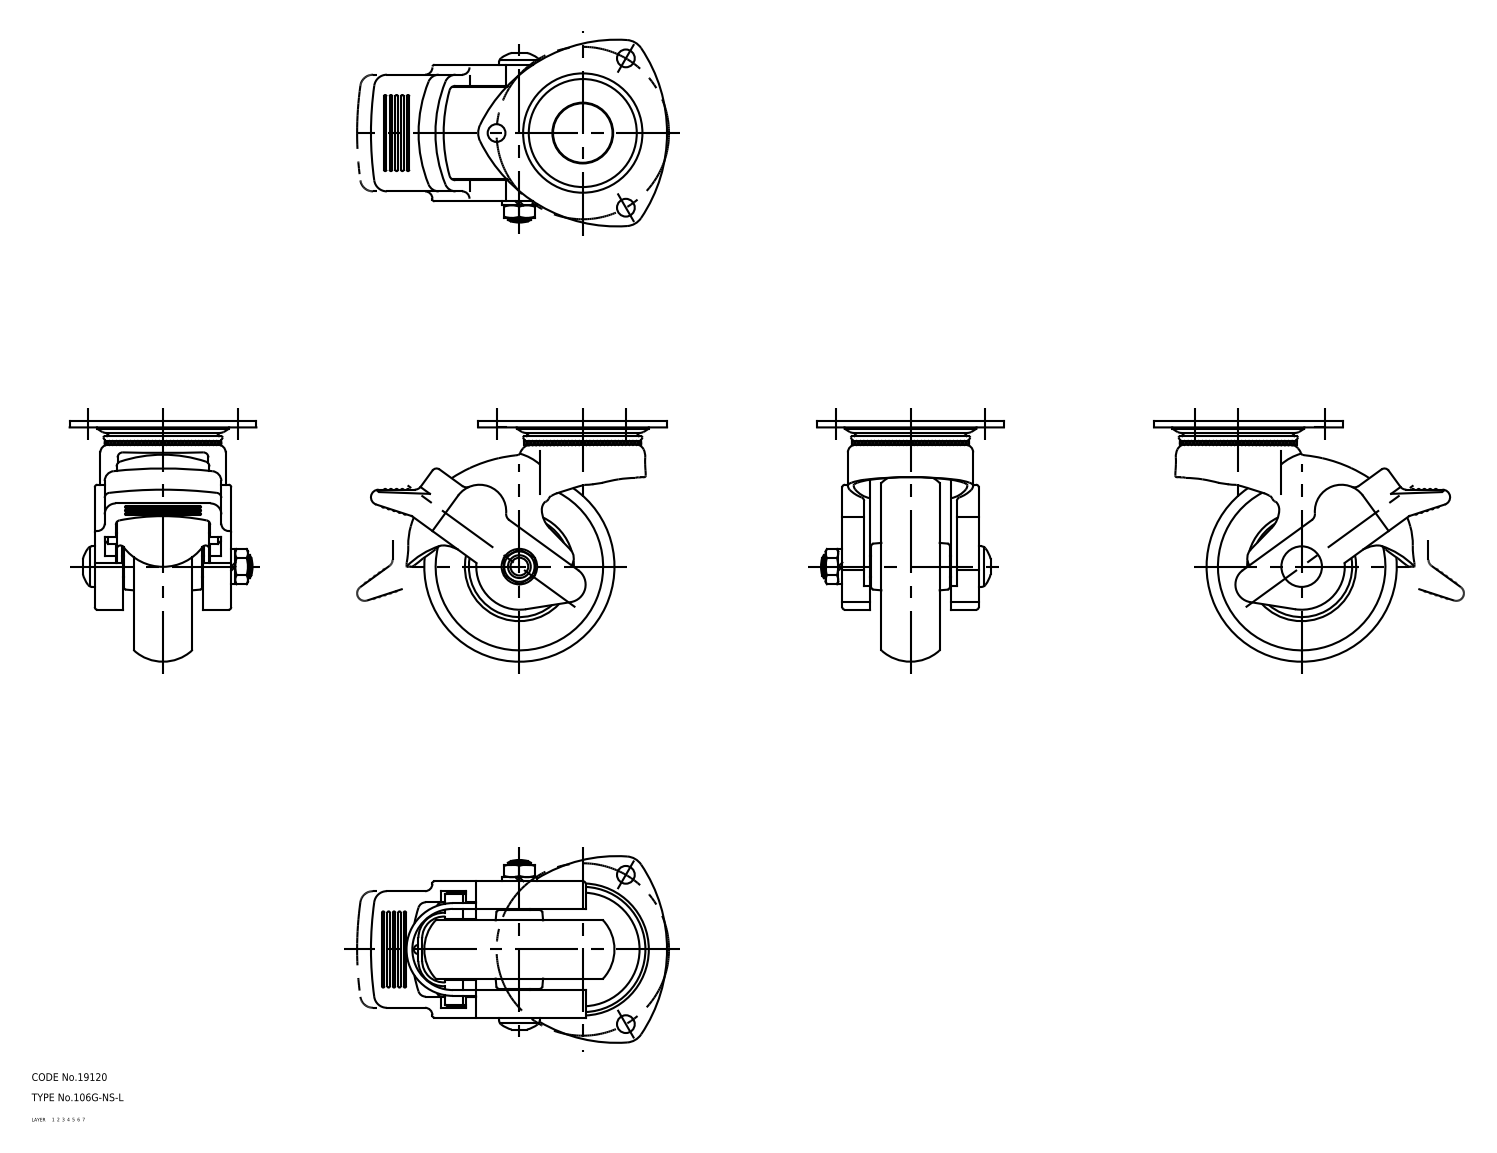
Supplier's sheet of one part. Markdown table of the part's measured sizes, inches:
| quantity | value |
| --- | --- |
| part name | lever; wheel; mounting plate; main shaft (+2 more) |
| STEP written by | CADfix (AUTOMOTIVE_DESIGN) |
| units | inches |
| bodies | 6 solids, 396 faces (0 planar, 0 cylindrical, 396 other) |
| overall size | 4.597 × 3.74 × 2.899 |
| volume | 9.924 in³ |
| surface area | 98.22 in² |
